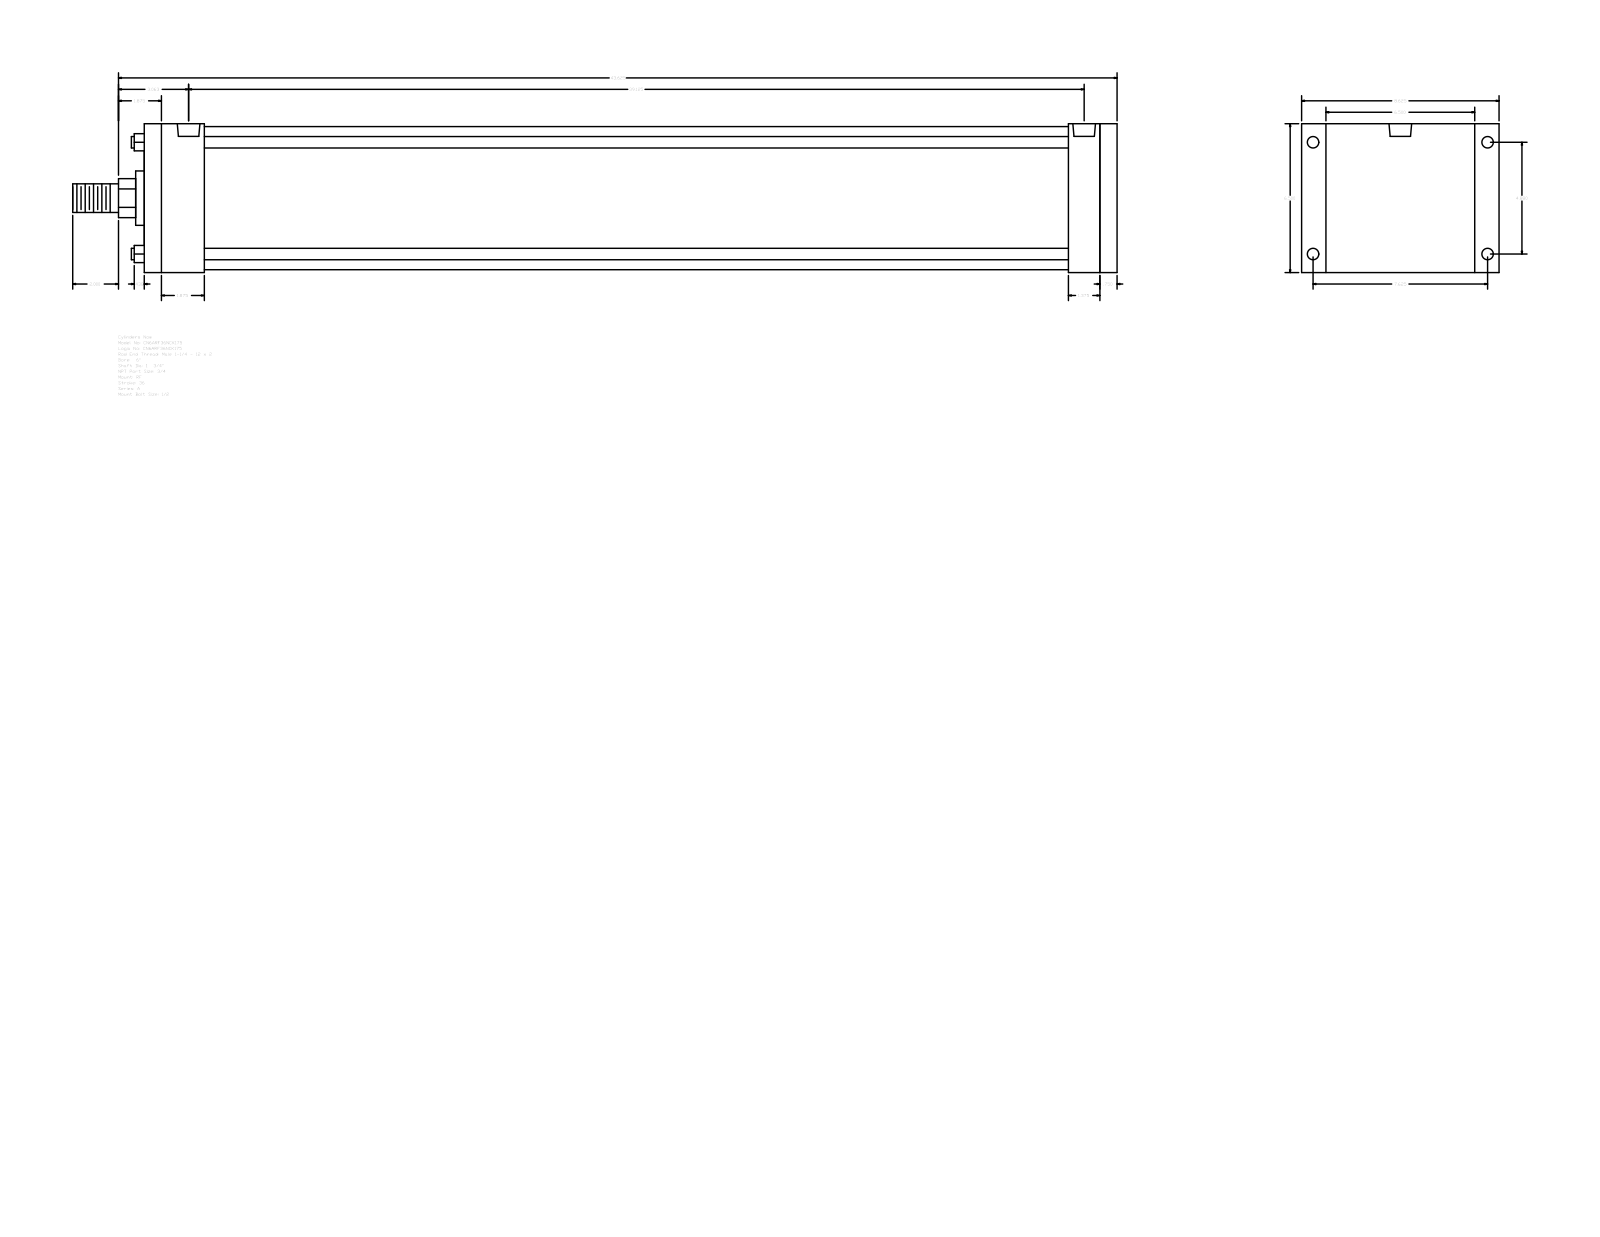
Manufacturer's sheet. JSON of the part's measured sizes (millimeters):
{"part_name": "A_RF__0600_1.75", "step_written_by": "GSSL Pune (CONFIG_CONTROL_DESIGN)", "units": "millimeters", "bodies": {"solids": 0, "faces": 92, "planar": 64, "cylindrical": 28, "other": 0}, "overall_size": [1158.88, 219.07, 165.1], "round_holes": [[12.7, 4], [15.08, 4], [25.12, 2]], "round_bosses_or_shafts": [[12.7, 4], [158.75, 1], [60.33, 1], [44.45, 1], [31.75, 1]], "partial_cylinders_radius": [[21.63, 1]], "face_to_face_distances": [165.1, 1079.51, 19.05, 1060.46, 66.68, 993.78, 1012.83, 1025.53, 958.85, 34.93], "hole_center_spacings": [5.56, 123.96, 193.68, 229.95, 982.65, 988.21, 993.77]}
